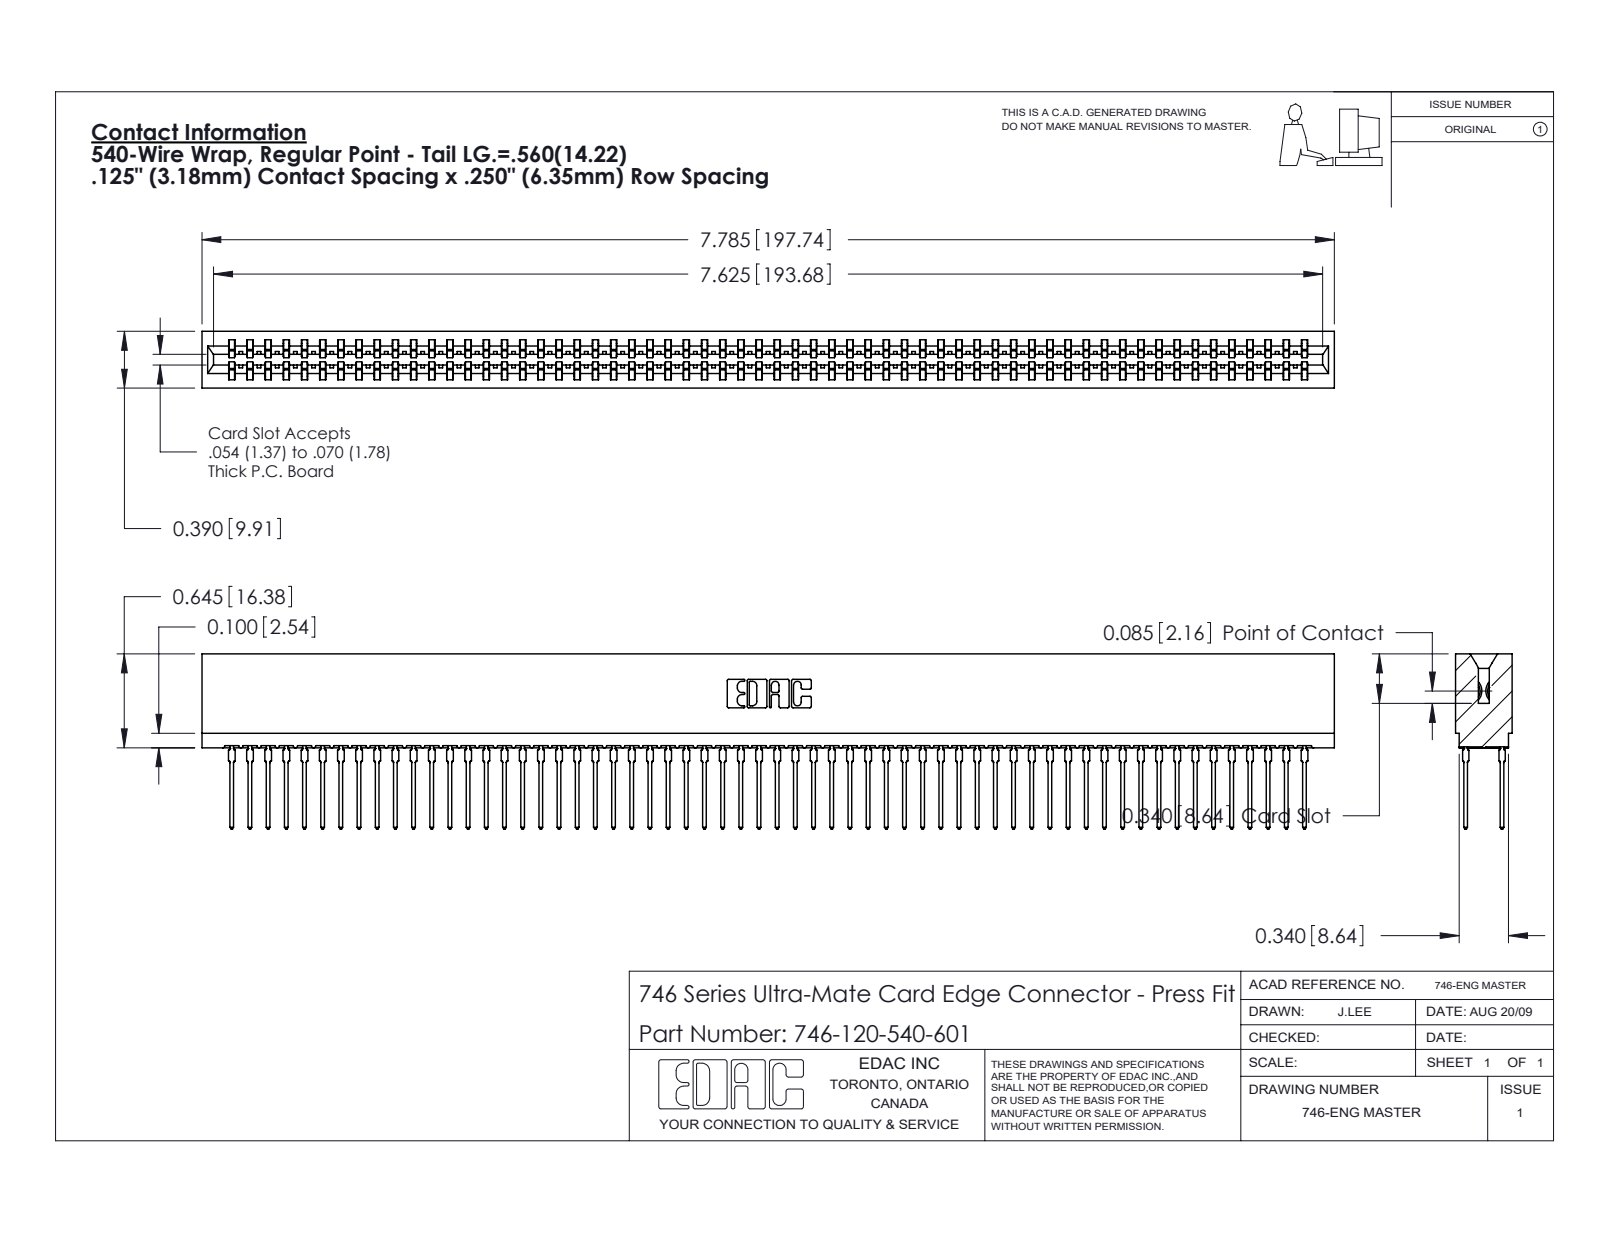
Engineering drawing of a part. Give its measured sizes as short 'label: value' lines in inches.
name: 746 Part_.340 Slot Depth - 01; 746-292-001_540; 746-120-540-601
written by: SolidWorks 2020 (CONFIG_CONTROL_DESIGN)
unit: in
bodies: 121 solids, 10837 faces (5575 planar, 2142 cylindrical, 3120 other)
size: 7.785 × 1.204 × 0.39
volume: 1.404 in³; area: 55.45 in²
rounds: 240× R0.021, 61× R0.015, 22× R0.01, 8× R0.005, 8× R0.011, 6× R0.007, 6× R0.031, 3× R0.026
face distances: 0.057, 0.333, 0.39, 0.025, 0.25, 0.307, 0.275, 0.083, 0.015, 0.059
